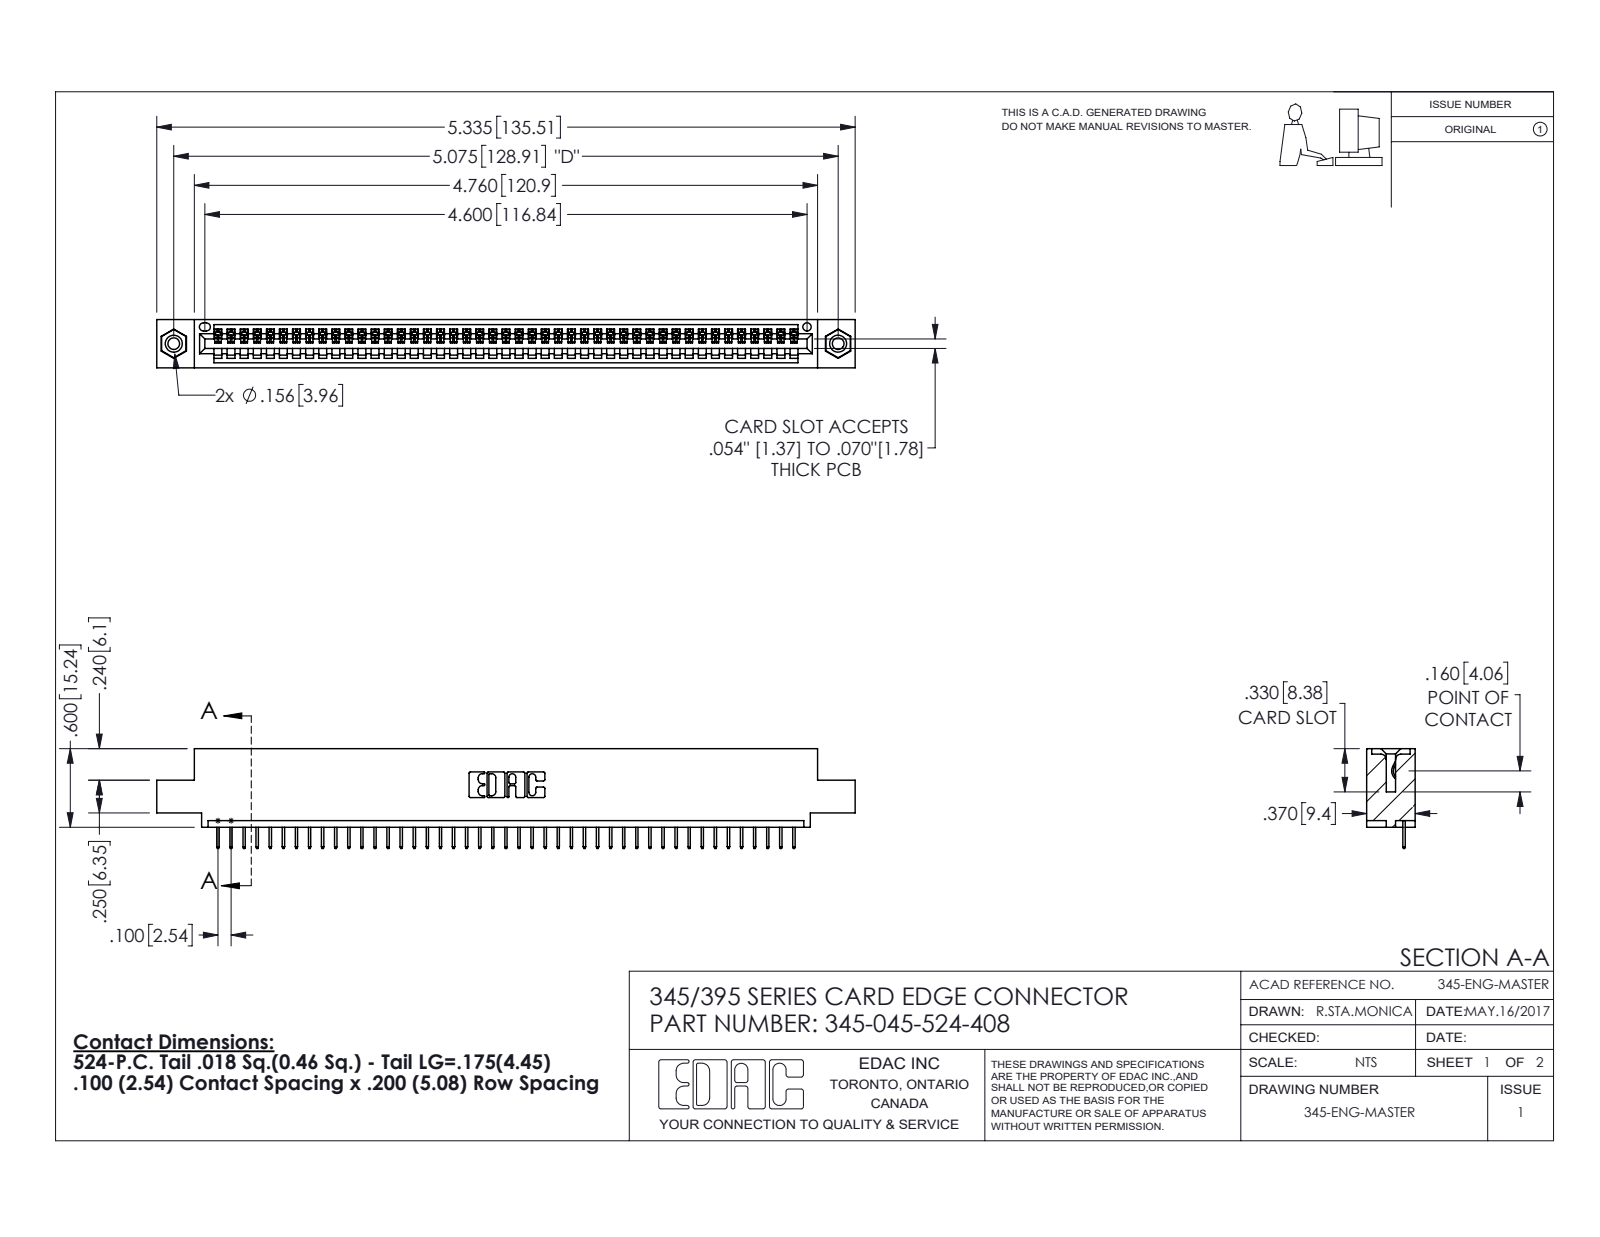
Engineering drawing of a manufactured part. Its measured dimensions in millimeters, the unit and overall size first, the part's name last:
Units: millimetres
Overall size (bounding box): 135.5 × 19.4 × 9.4
Round holes (diameter × count): ⌀2.3 ×2, ⌀3.2 ×2, ⌀4 ×2, ⌀1.6 ×1
Round bosses / shafts (diameter × count): ⌀3.9 ×2
Partial cylindrical surfaces — rounded edges, fillets, slot ends (radius × count): R0.2 ×90, R0.3 ×22, R0.2 ×6, R0.8 ×6, R0.7 ×3, R0.8 ×2, R1 ×2, R0.4 ×1
Main face-to-face distances: 1.8, 7.6, 9.4, 5.1, 2.5, 6.9, 0.6, 5.7, 1.8, 3.8
Hole centre spacings: 6.9, 122.9, 128.9
Volume: 12 600 mm³ · Surface area: 16 370 mm²
Bodies: 48 solids, 2980 faces (2186 planar, 778 cylindrical, 16 other)
Part name (STEP PRODUCT): 345-292-001_345-293-124; 345-045-524-408; 345-250-001_345-250-003-102; 345 Part_0.110 Offset - 0.156 Dia-TI
STEP written by: SolidWorks 2016 (CONFIG_CONTROL_DESIGN)
